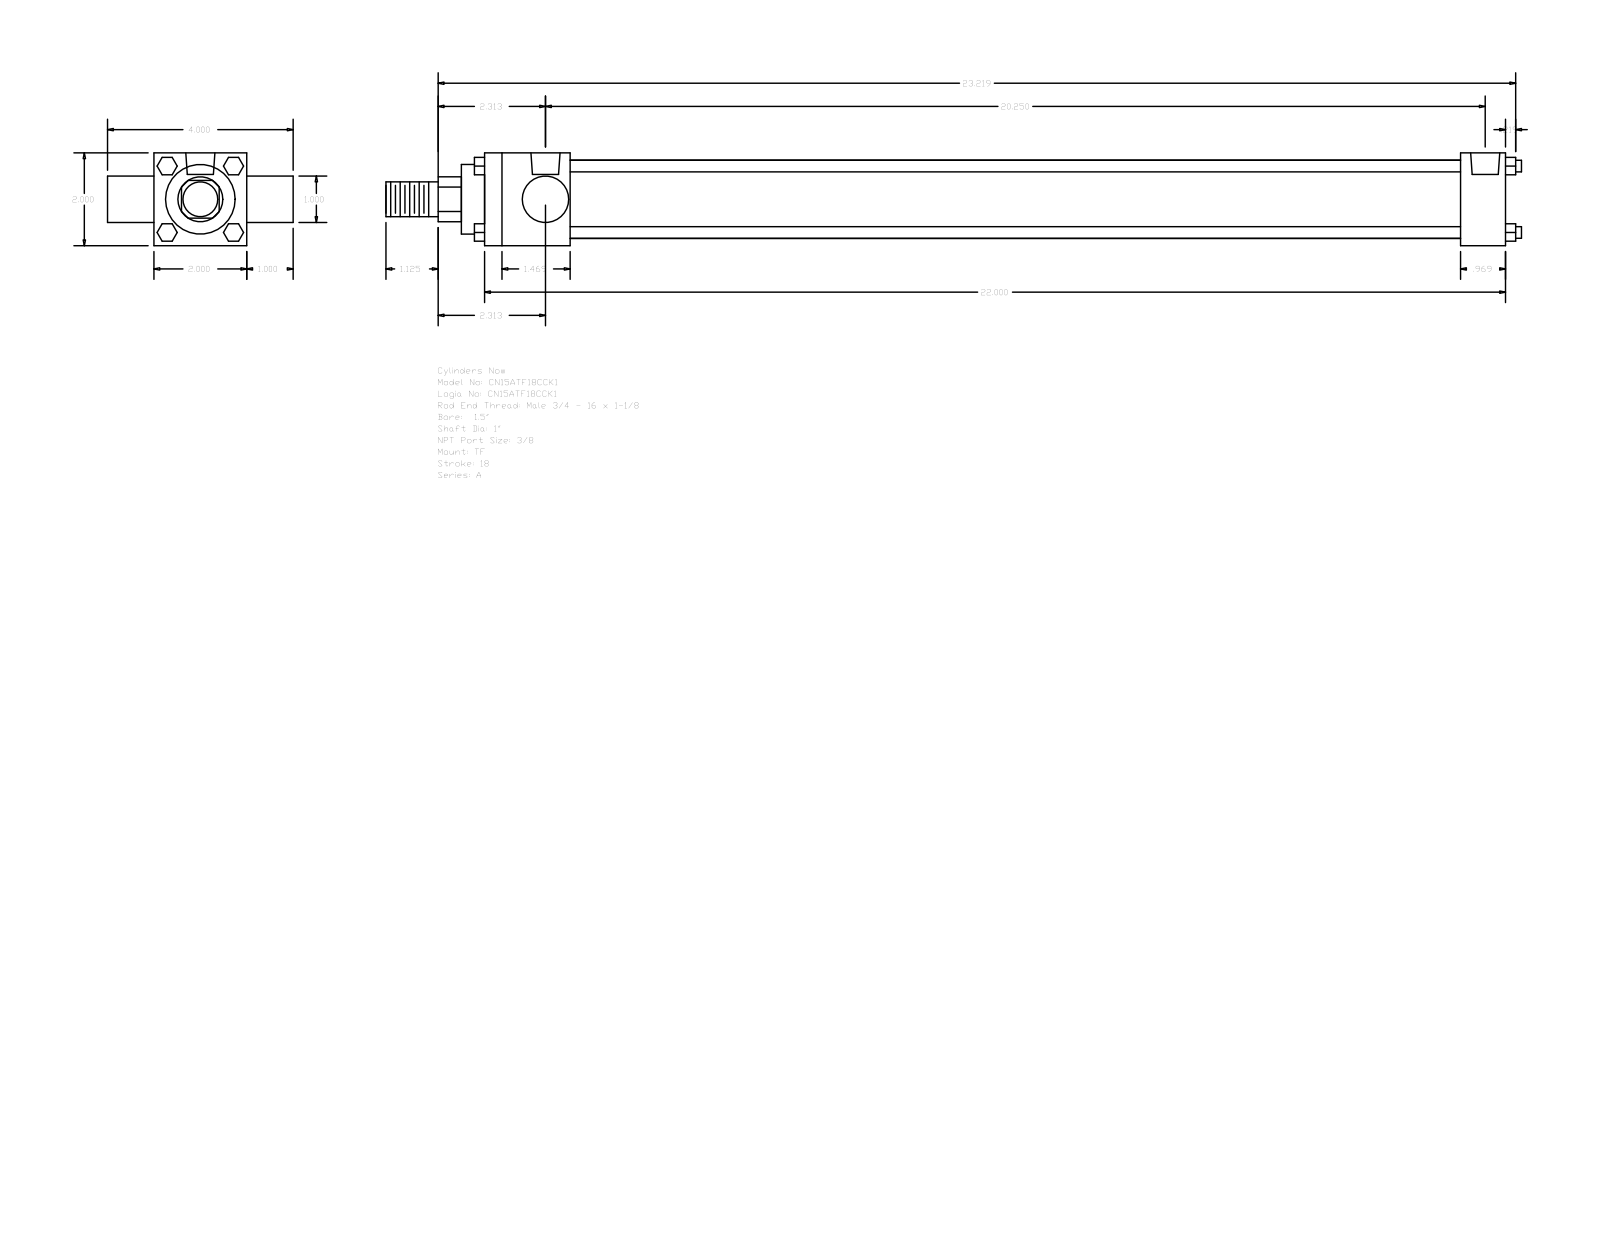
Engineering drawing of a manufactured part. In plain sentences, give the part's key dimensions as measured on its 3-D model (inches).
The part is named "A_TF__0150_1". Its 3-D file was written by "GSSL Pune (CONFIG_CONTROL_DESIGN)". It is 0 solids with 120 faces: 92 planar, 28 cylindrical and 0 other. Overall it measures 24.469 by 4 by 2 inches. Round holes: 3 of diameter 0.219, 2 of diameter 0.627. Round bosses or shafts: 4 of diameter 0.25, 2 of diameter 1, 1 of diameter 1.69, 1 of diameter 1.5, 1 of diameter 0.75. Partial cylindrical surfaces (rounded edges, fillets, slot ends): 1 of radius 0.484. The main face-to-face distances are 2, 1, 22, 3, 1.844, 21.031, 19.187, 20.156, 0.969, 0.5. The hole center spacings are 0.156, 20.094, 19.937, 20.25.
